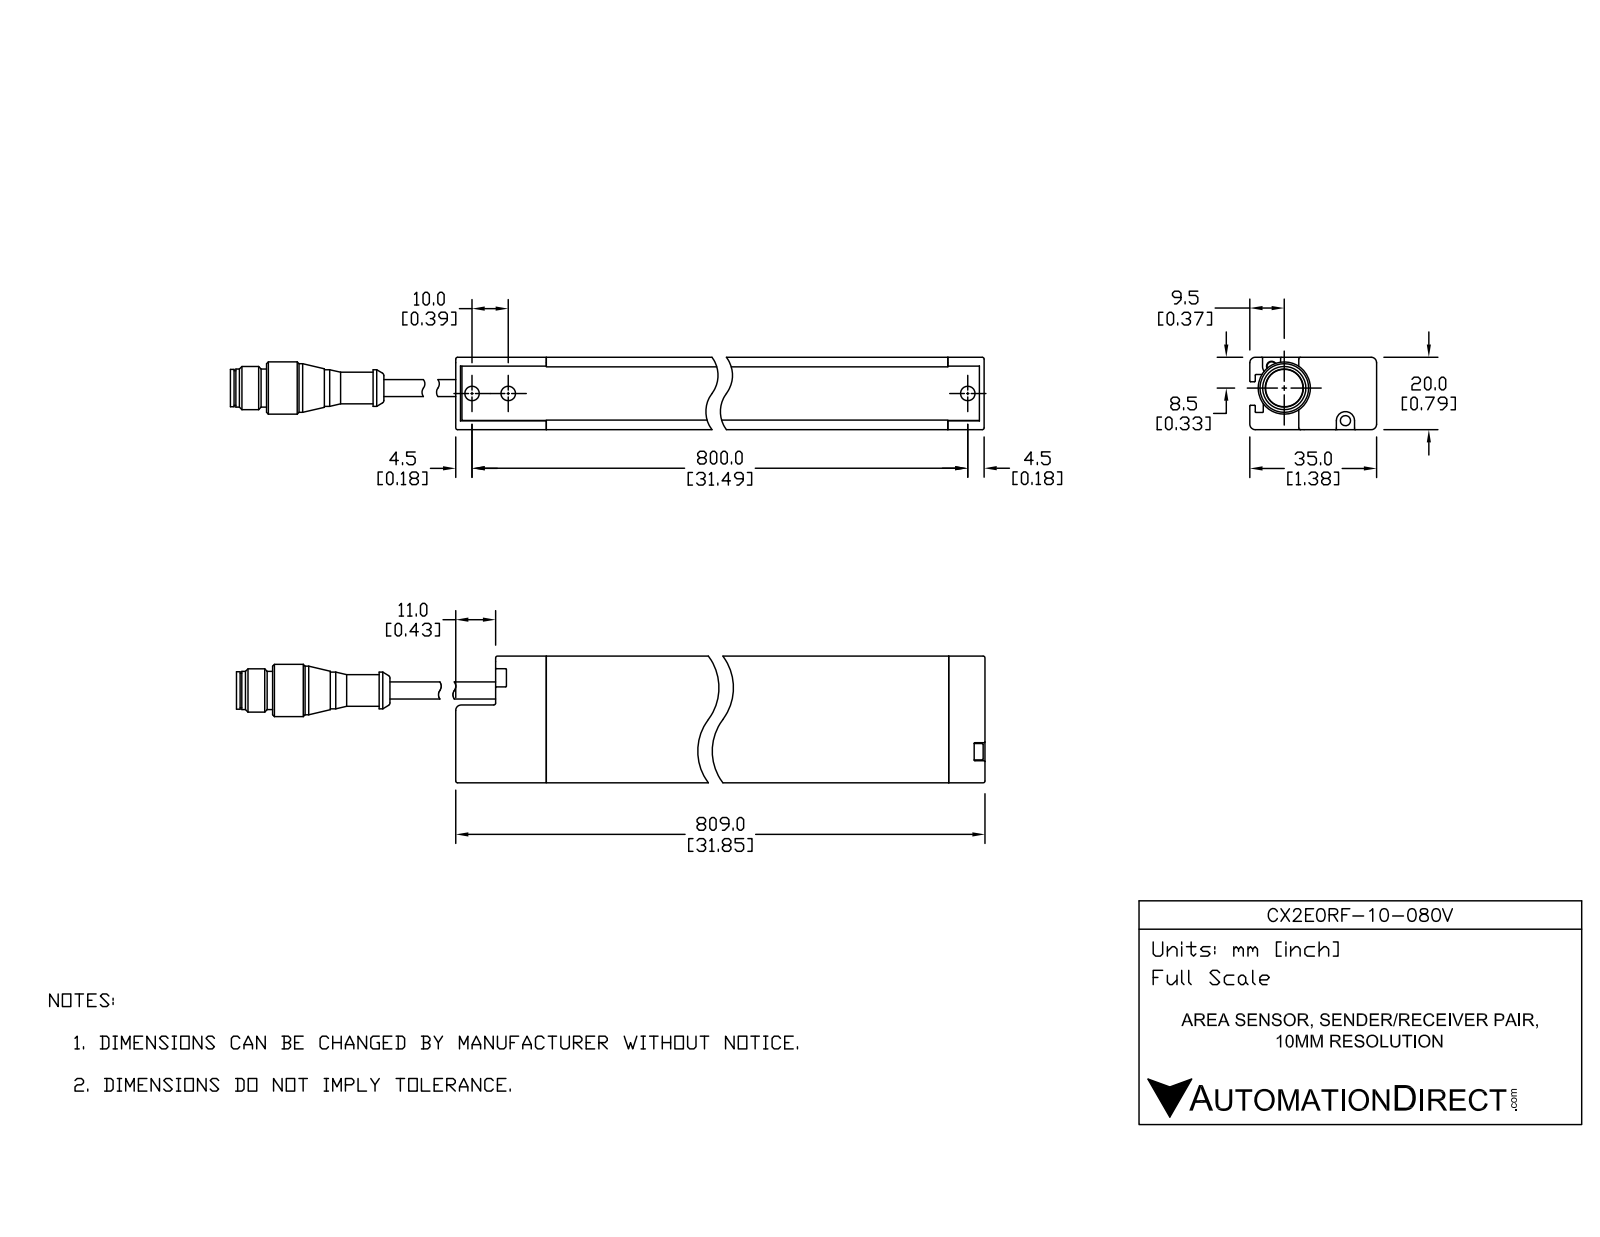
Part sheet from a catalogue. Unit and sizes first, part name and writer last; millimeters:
Units: millimetres
Overall size (bounding box): 886.84 × 507.67 × 156.28
Round holes (diameter × count): ⌀2.8 ×8, ⌀6.5 ×2, ⌀8 ×2
Round bosses / shafts (diameter × count): ⌀2.01 ×8, ⌀14.42 ×2, ⌀13.42 ×2, ⌀11.93 ×2, ⌀10.53 ×2, ⌀10.33 ×2, ⌀10.13 ×2, ⌀9.53 ×2
Partial cylindrical surfaces — rounded edges, fillets, slot ends (radius × count): R0.2 ×96, R0.5 ×26, R1.5 ×10, R2.5 ×8, R0.3 ×4
Main face-to-face distances: 136.29, 20, 2, 156.29, 116.29, 439.34, 30.9, 469.37, 3.7, 34.6
Hole centre spacings: 15, 20.4, 25.32, 494.43, 6.95, 9.66, 17.93, 19.15
Volume: 1 119 000 mm³ · Surface area: 266 328 mm²
Bodies: 14 solids, 638 faces (206 planar, 262 cylindrical, 170 other)
STEP written by: Unknown (AUTOMOTIVE_DESIGN)
